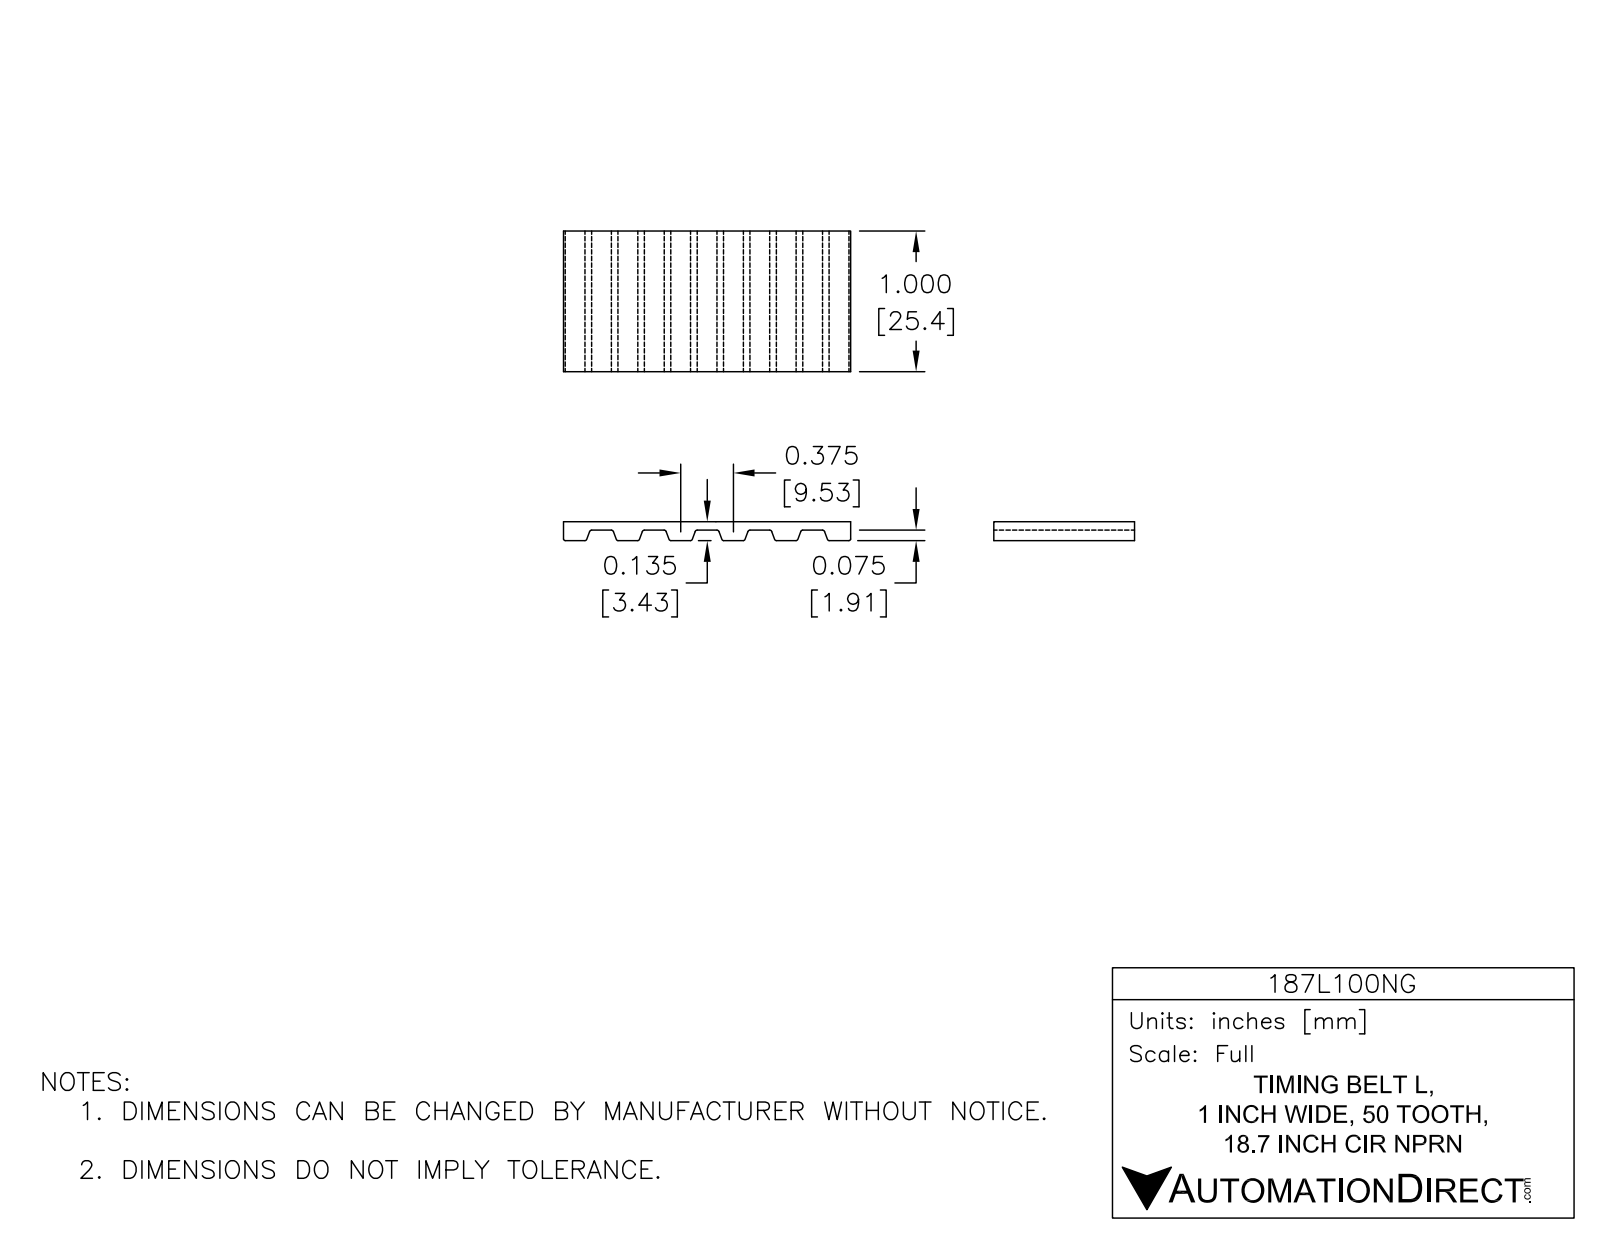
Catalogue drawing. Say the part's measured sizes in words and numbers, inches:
The part is named "187L100NG". Its 3-D file was written by "SolidWorks 2014 (AUTOMOTIVE_DESIGN)". It is 1 solid with 417 faces: 176 planar, 241 cylindrical and 0 other. Overall it measures 7.663 by 3 by 1 inches. Its volume is 1.684 cubic inches and its surface area 44.89 square inches. Partial cylindrical surfaces (rounded edges, fillets, slot ends): 196 of radius 0.02, 2 of radius 1.435, 2 of radius 1.5. The main face-to-face distances are 0.065, 2.935, 3, 2.87, 0.14, 2.86, 0.075, 2.795, 1, 0.352.
